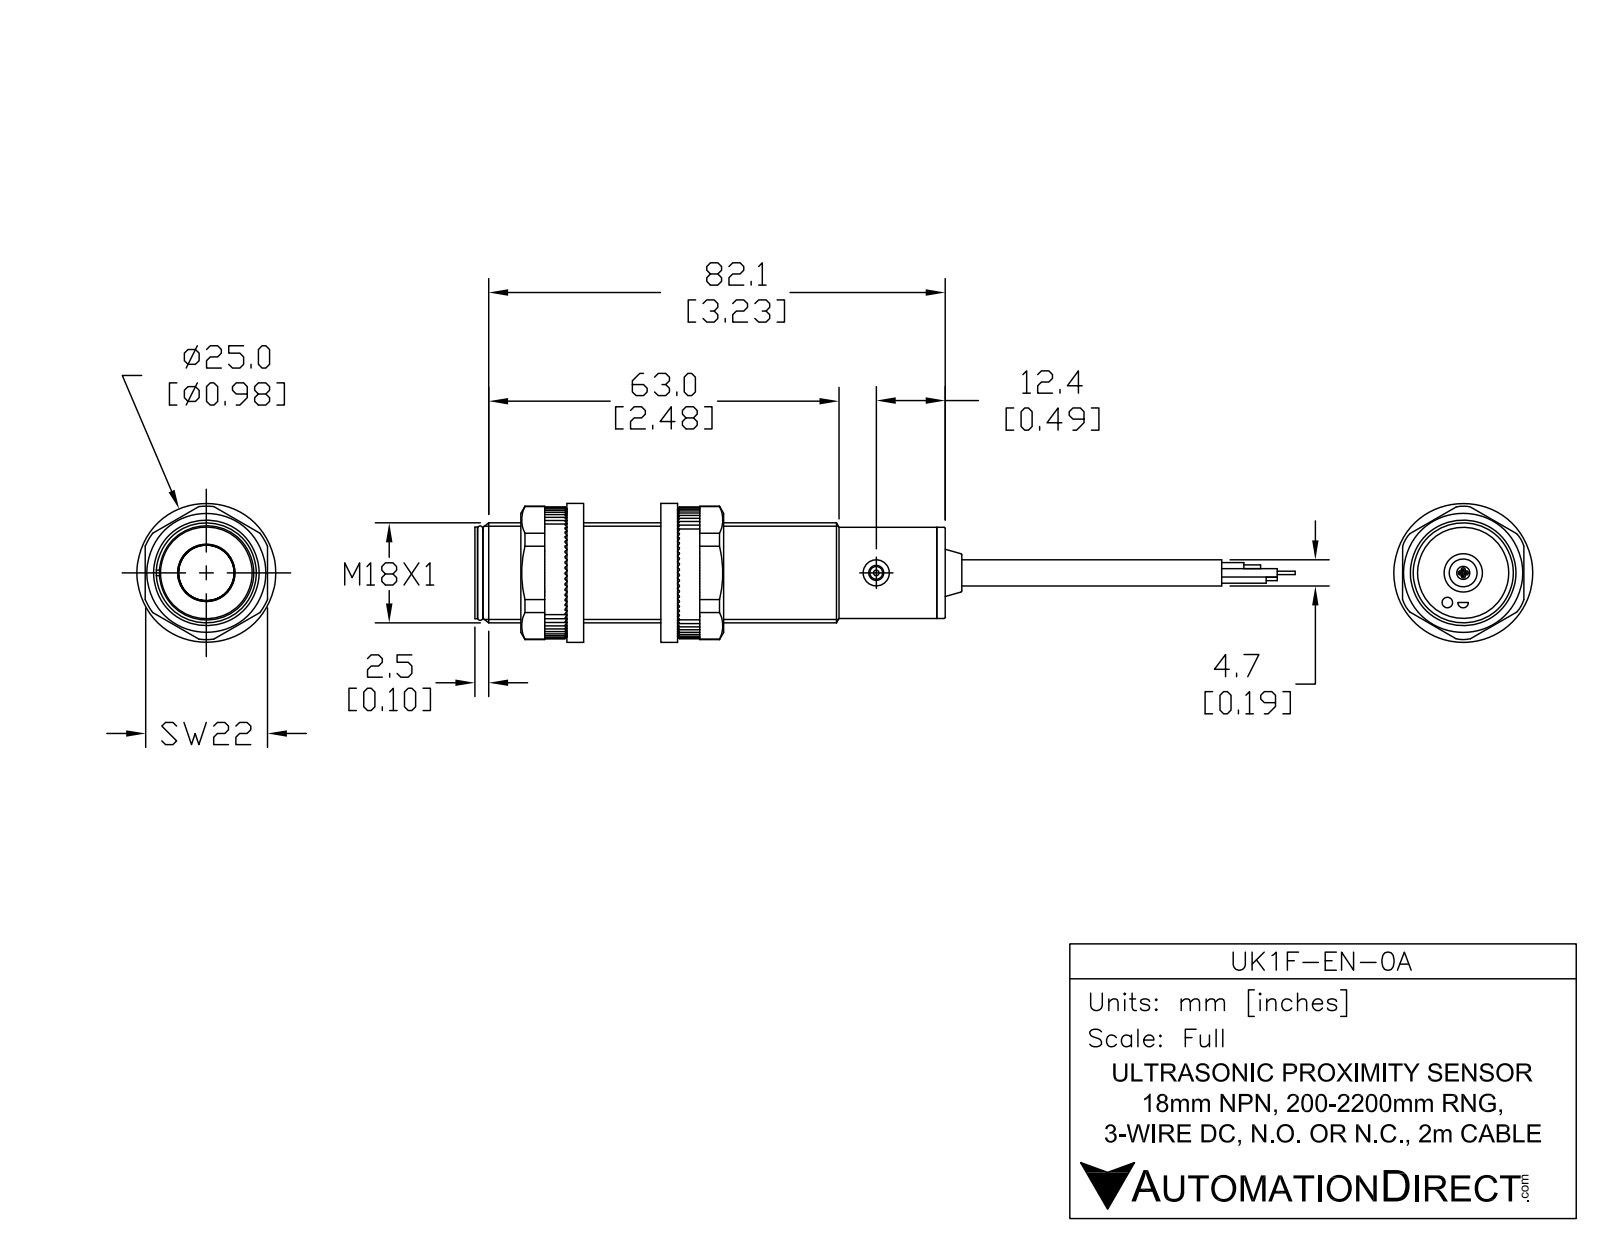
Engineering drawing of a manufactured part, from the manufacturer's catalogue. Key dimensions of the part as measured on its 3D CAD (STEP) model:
Part name (STEP PRODUCT): UK1F-EN-0A
STEP written by: SolidWorks 2017 (AUTOMOTIVE_DESIGN)
Units: inches
Bodies: 6 solids, 55 faces (17 planar, 24 cylindrical, 14 other)
Overall size (bounding box): 4.832 × 0.709 × 0.709
Volume: 1.285 in³ · Surface area: 10.69 in²
Round holes (diameter × count): ⌀0.185 ×2, ⌀0.106 ×1
Round bosses / shafts (diameter × count): ⌀0.709 ×1, ⌀0.646 ×1, ⌀0.622 ×1, ⌀0.374 ×1, ⌀0.189 ×1, ⌀0.091 ×1
Main face-to-face distances: 3.193, 3.252, 0.059, 0.039, 3.232, 3.291, 0.041, 3.234, 3.293, 3.257
